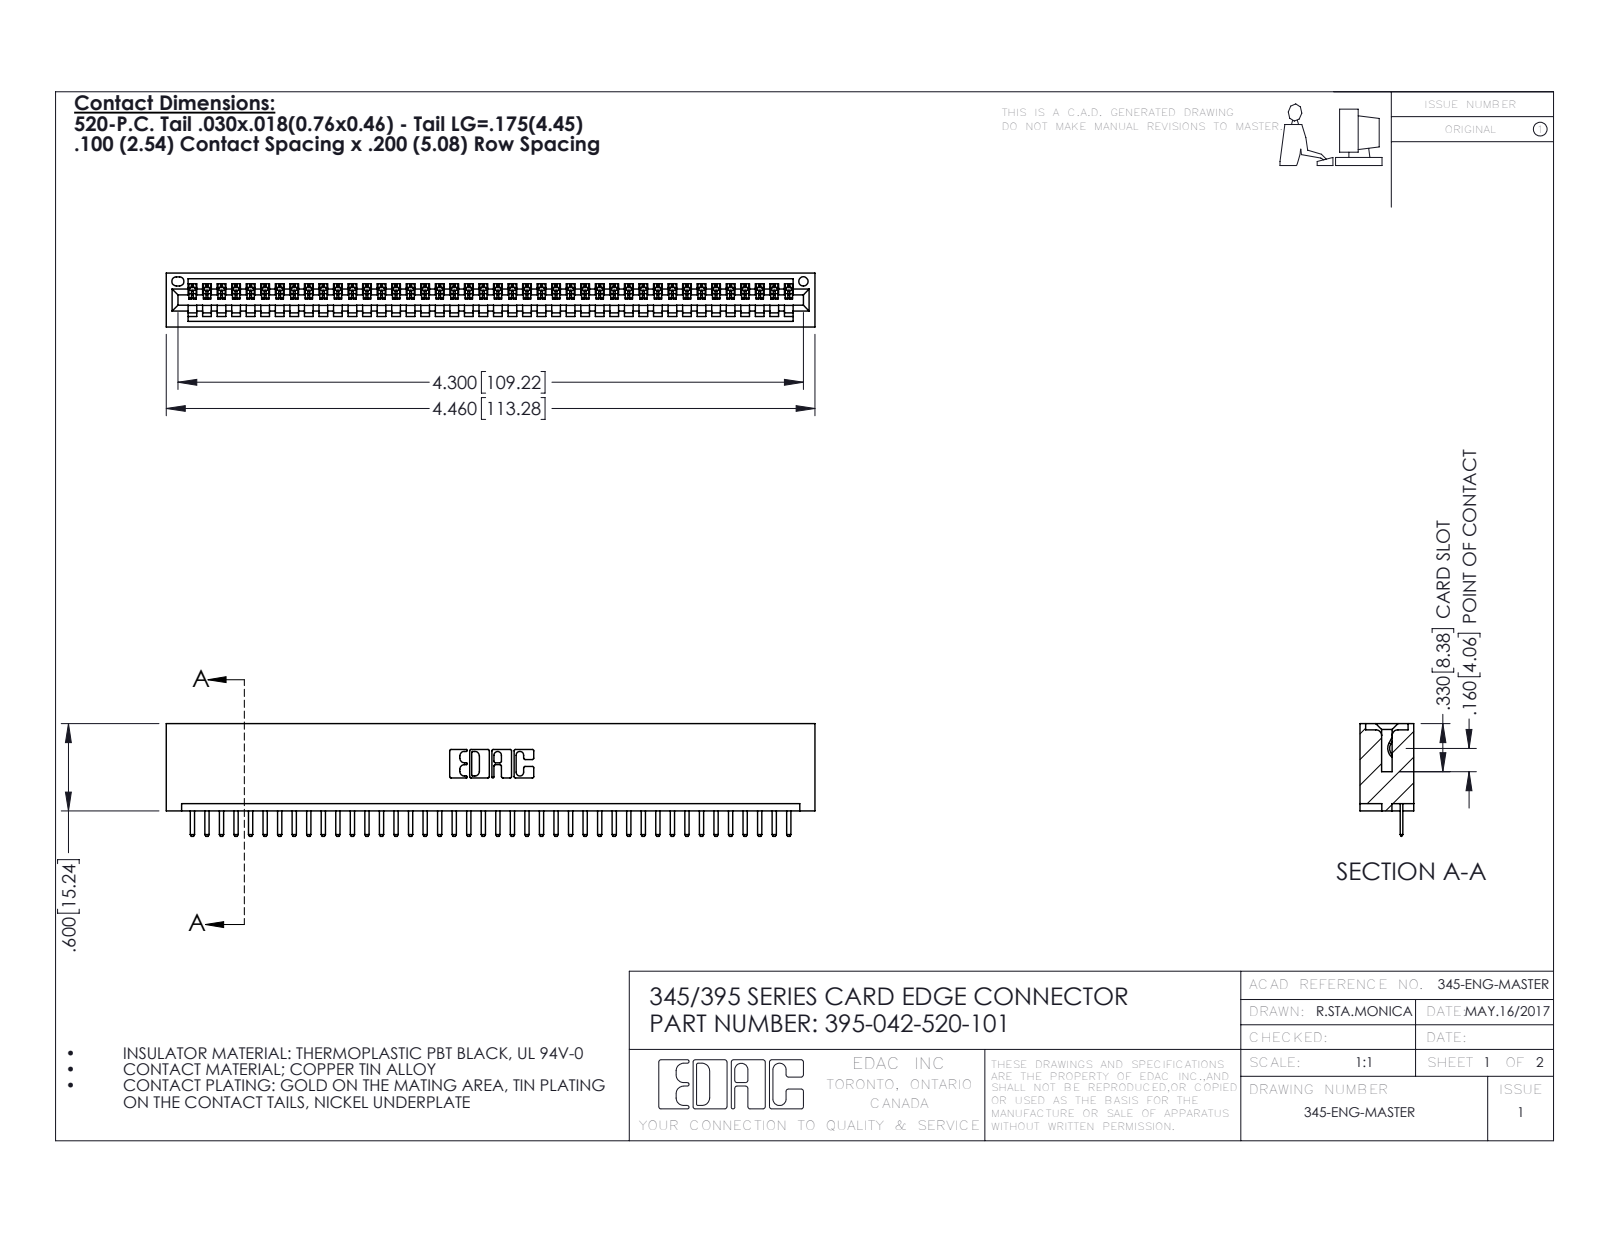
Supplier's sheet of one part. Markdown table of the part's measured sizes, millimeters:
| quantity | value |
| --- | --- |
| part name | 345-292-001_345-293-120; 395-042-520-101; 345 Part_No Mounting Lugs |
| STEP written by | SolidWorks 2016 (CONFIG_CONTROL_DESIGN) |
| units | millimeters |
| bodies | 43 solids, 2722 faces (1840 planar, 882 cylindrical, 0 other) |
| overall size | 113.3 × 19.7 × 9.4 |
| volume | 11 200 mm³ |
| surface area | 14 710 mm² |
| round holes (diameter × count) | 1.6 × 1 |
| partial cylindrical surfaces (radius × count) | 0.3 × 86, 0.2 × 84, 0.3 × 22, 0.2 × 6, 0.8 × 6, 0.7 × 3, 0.8 × 2, 1 × 2 |
| main face-to-face distances | 7.6, 1.8, 9.4, 5.1, 2.5, 6.9, 0.6, 5.7, 1.8, 3.8 |
